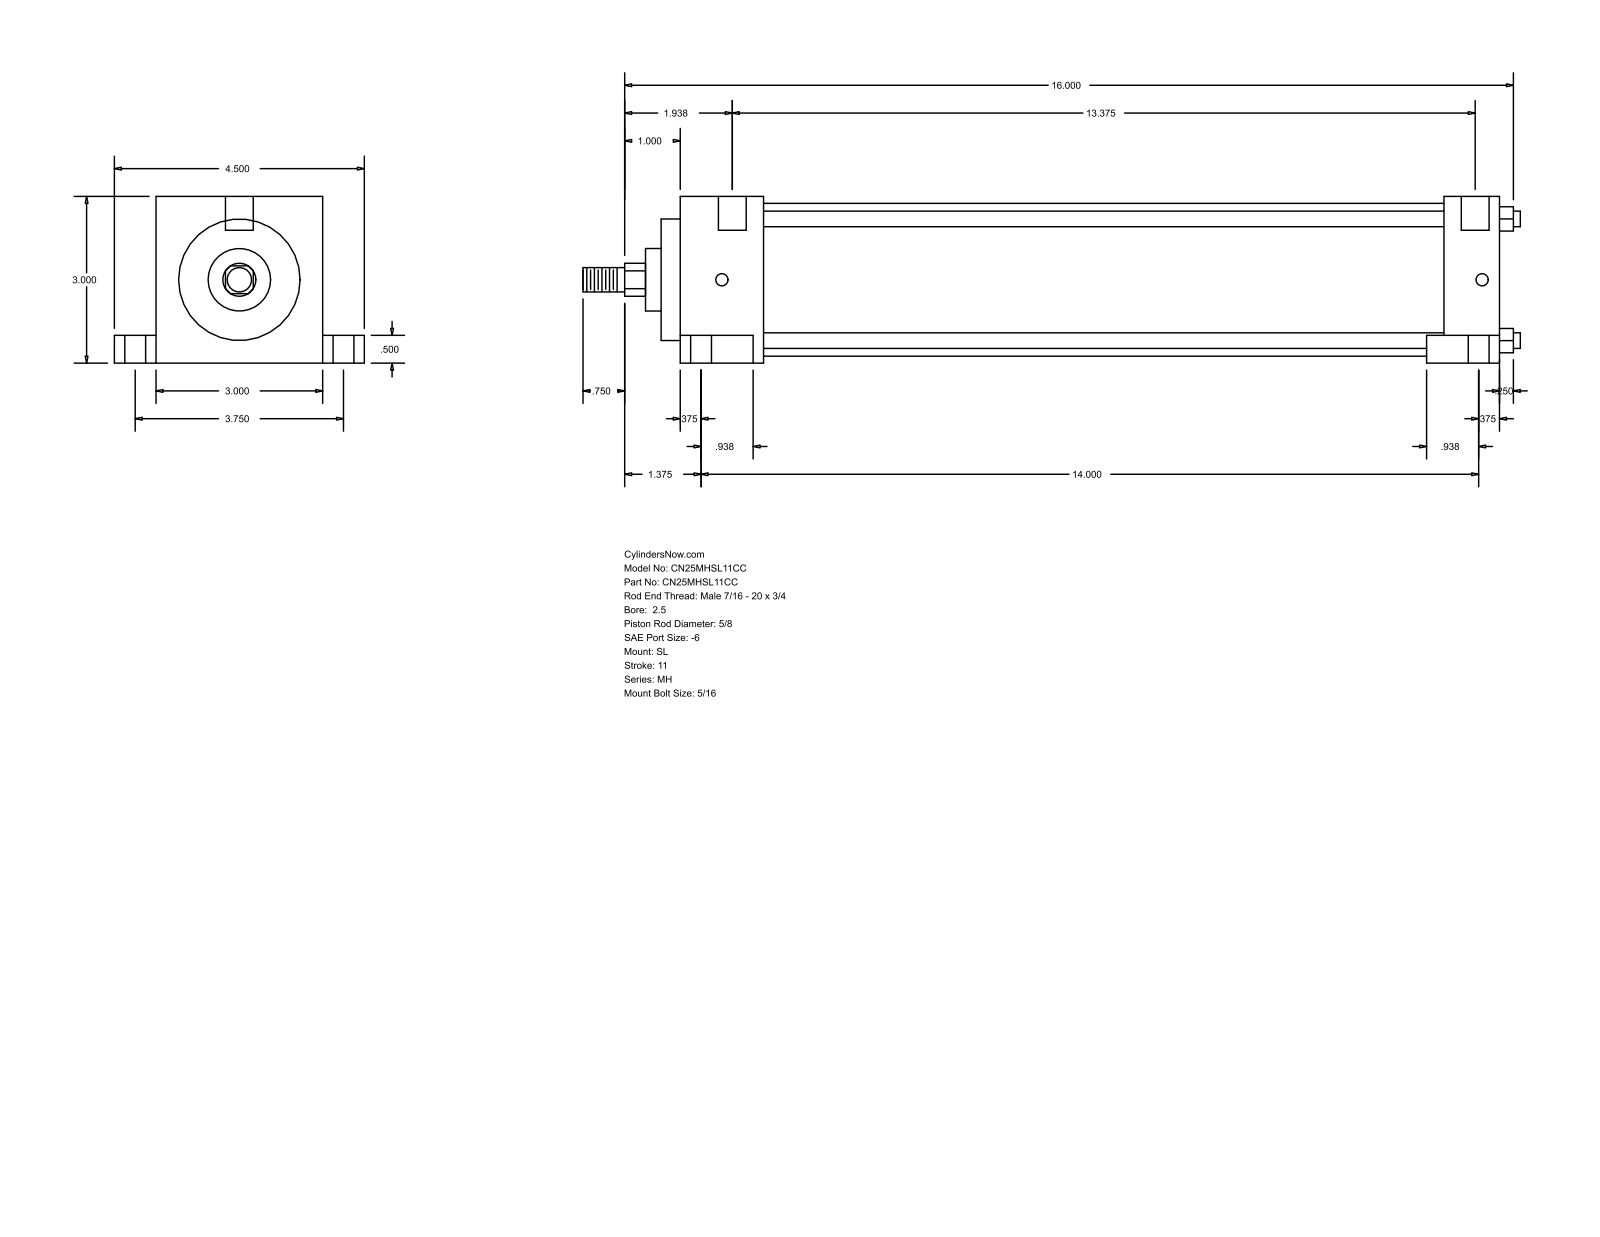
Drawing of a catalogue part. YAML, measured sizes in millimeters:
part_name: "MH_SL__0250_0.625"
step_written_by: "GSSL Pune (CONFIG_CONTROL_DESIGN)"
units: millimeters
bodies: {solids: 0, faces: 86, planar: 61, cylindrical: 25, other: 0}
overall_size: [428.62, 114.3, 76.2]
round_holes:
  - {diameter: 5.56, count: 2}
  - {diameter: 9.53, count: 2}
  - {diameter: 15.88, count: 2}
  - {diameter: 12.7, count: 1}
round_bosses_or_shafts:
  - {diameter: 7.14, count: 4}
  - {diameter: 69.85, count: 1}
  - {diameter: 55.55, count: 1}
  - {diameter: 28.57, count: 1}
  - {diameter: 15.88, count: 1}
  - {diameter: 11.11, count: 1}
partial_cylinders:
  - {radius: 7.54, count: 1}
face_to_face_distances: [76.2, 25.4, 357.98, 383.38, 63.5, 12.7, 19.05, 95.25, 31.75, 350.04]
hole_center_spacings: [47.65, 3.17, 95.24]
